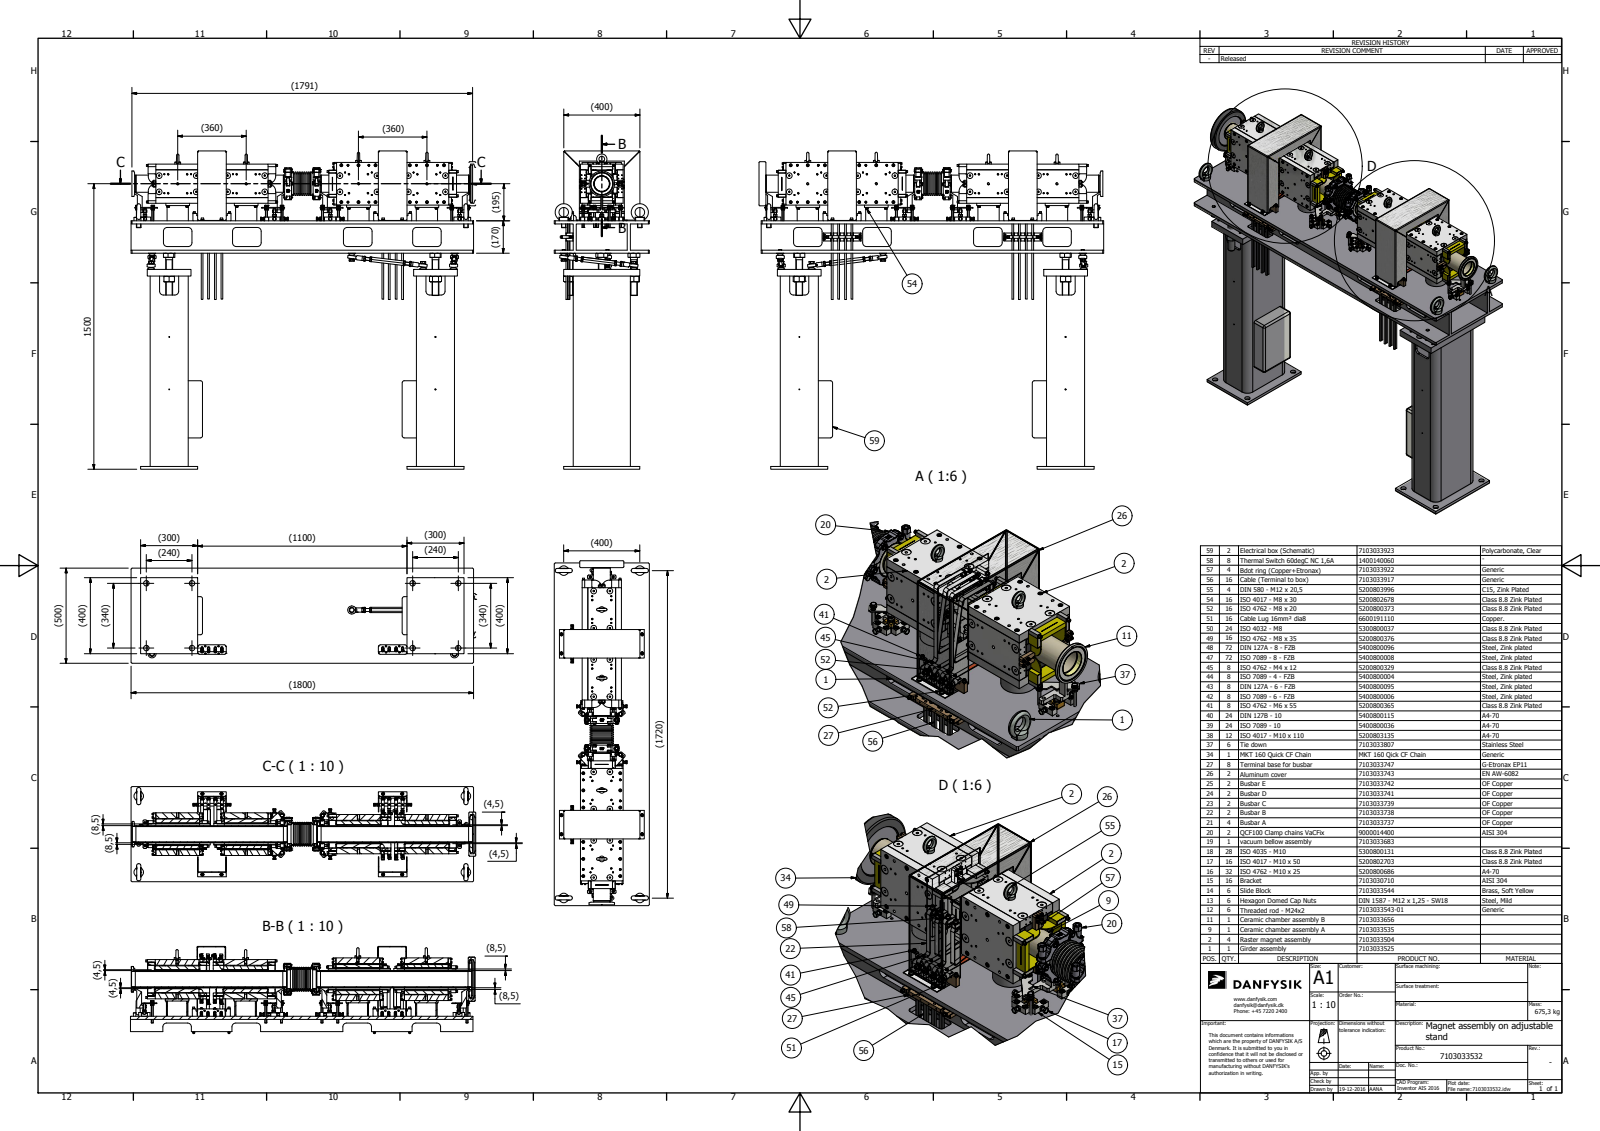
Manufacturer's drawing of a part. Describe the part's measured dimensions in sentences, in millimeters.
The part is named "7103033526; 7103033528; 5200802918; 5300800049 (+8 more)". Its 3-D file was written by "Autodesk Inventor 2016 (AUTOMOTIVE_DESIGN)". It is 2363 solids with 64647 faces: 35266 planar, 16615 cylindrical and 12766 other. Overall it measures 1800 by 1672 by 552 millimeters. Its volume is 114 000 000 cubic millimeters and its surface area 26 810 000 square millimeters. Round holes: 128 of diameter 1.4, 104 of diameter 3.24, 96 of diameter 1.2, 90 of diameter 4, 88 of diameter 6.65, 88 of diameter 7, 88 of diameter 9, 64 of diameter 2, 64 of diameter 2.46, 64 of diameter 3.2, 64 of diameter 3.96, 62 of diameter 4.92. Round bosses or shafts: 117 of diameter 6, 107 of diameter 10, 86 of diameter 16, 80 of diameter 11.8, 78 of diameter 8, 72 of diameter 12, 72 of diameter 0.8, 68 of diameter 3. Partial cylindrical surfaces (rounded edges, fillets, slot ends): 864 of radius 0.5, 600 of radius 1, 384 of radius 0.28, 384 of radius 0.49, 146 of radius 2, 132 of radius 1.52, 128 of radius 0.45, 128 of radius 0.89. The main face-to-face distances are 16, 10, 154, 1.2, 138, 170, 210, 200, 1390, 1400. The hole center spacings are 18, 950, 25.46, 158, 194.83, 36, 40.25, 100.
